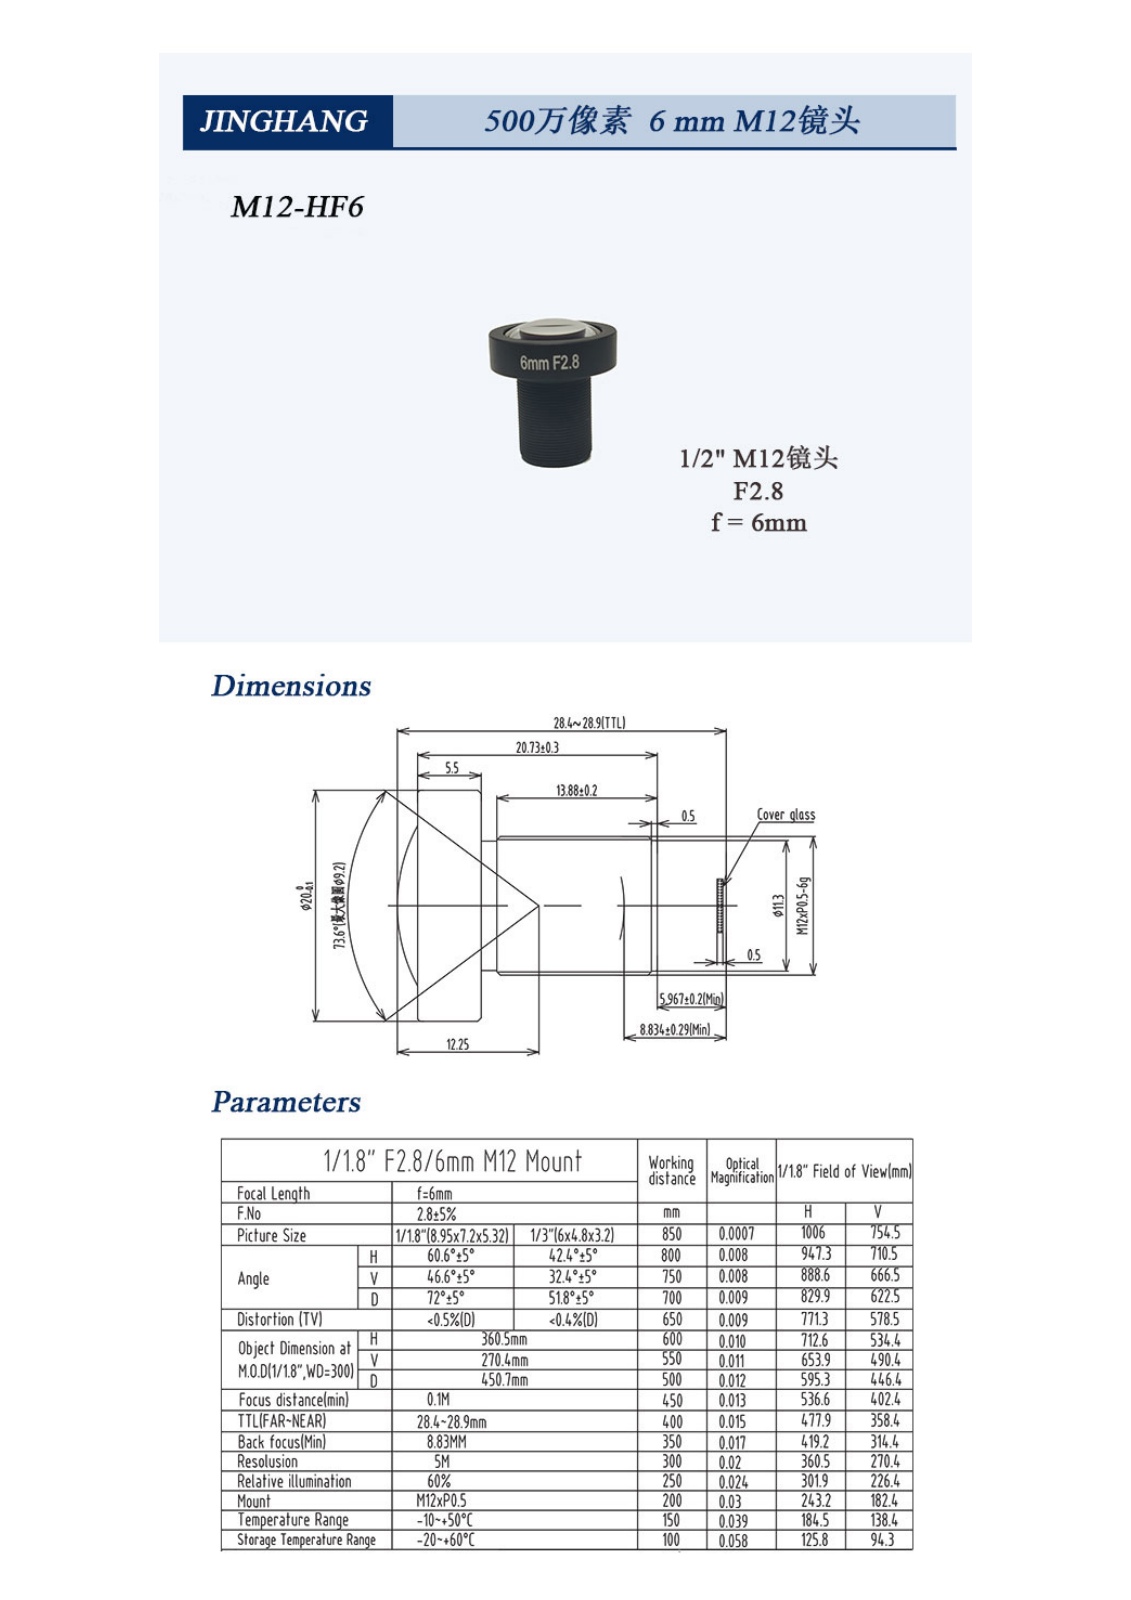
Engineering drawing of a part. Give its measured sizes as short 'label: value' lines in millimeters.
name: FS0605A-200
written by: PRO/ENGINEER BY PARAMETRIC TECHNOLOGY CORPORATION, 2010370 (CONFIG_CONTROL_DESIGN)
unit: mm
bodies: 1 solid, 121 faces (8 planar, 65 cylindrical, 48 other)
size: 22.48 × 20 × 20
volume: 3 417 mm³; area: 2 020 mm²
holes: 1× ⌀10, 1× ⌀15.4, 1× ⌀18.2
bosses: 1× ⌀20, 1× ⌀18, 1× ⌀12, 1× ⌀11.3, 1× ⌀11.2
face distances: 5.35, 20.52, 15.17, 5.5, 15.02, 20.72, 15.37, 15.22, 1.35, 1.5
